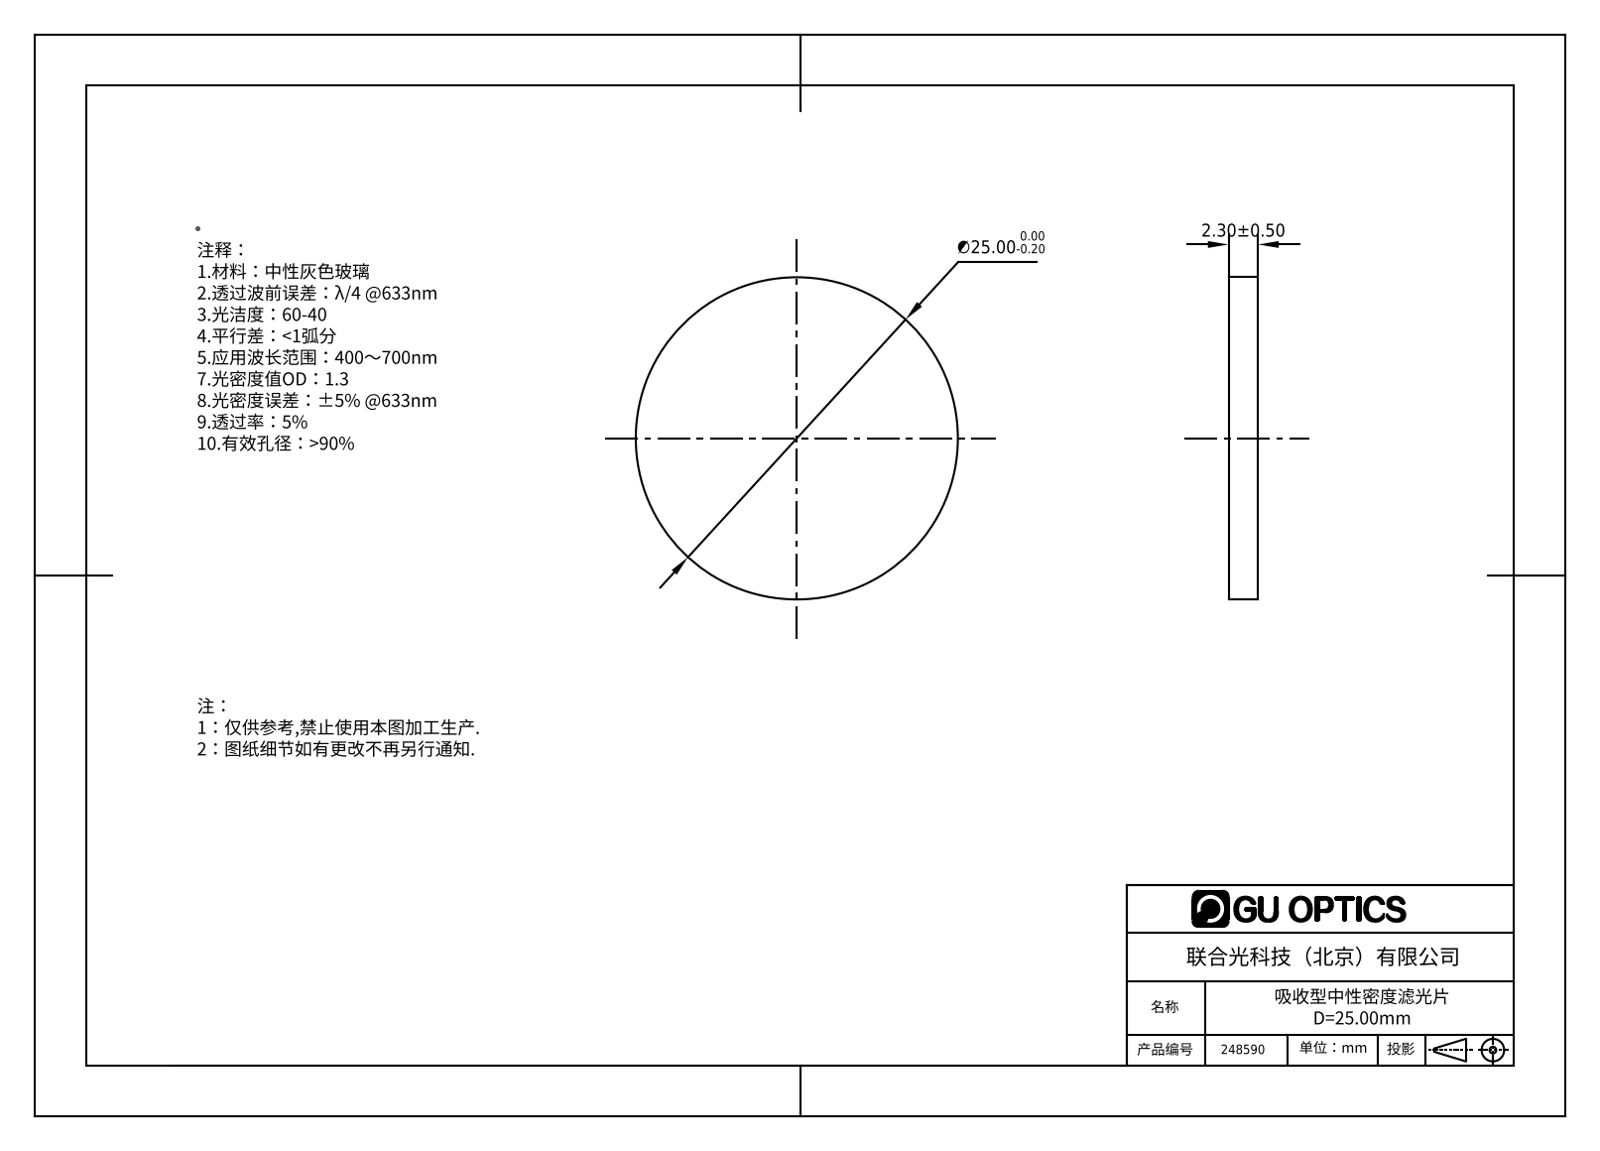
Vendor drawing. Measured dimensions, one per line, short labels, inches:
name: 248590
written by: SolidWorks 2016 (AUTOMOTIVE_DESIGN)
unit: in
bodies: 1 solid, 4 faces (2 planar, 2 cylindrical, 0 other)
size: 0.984 × 0.984 × 0.091
volume: 0.069 in³; area: 1.801 in²
bosses: 1× ⌀0.984
face distances: 0.091
